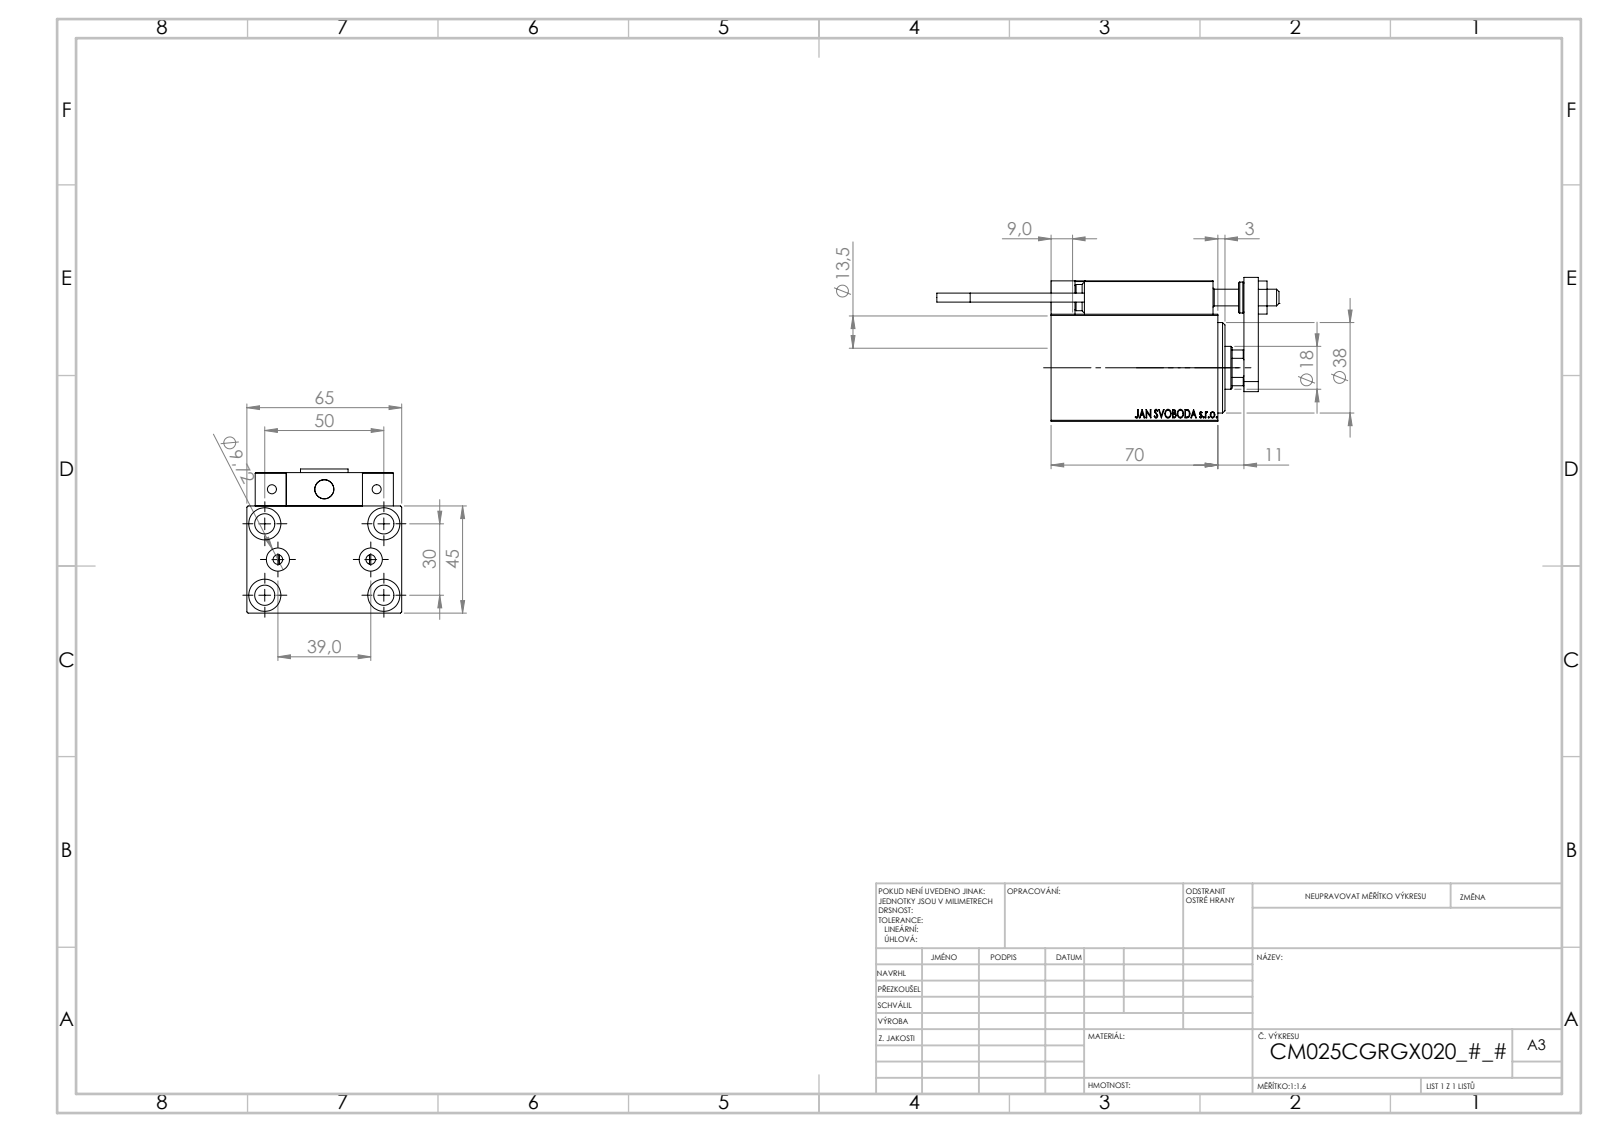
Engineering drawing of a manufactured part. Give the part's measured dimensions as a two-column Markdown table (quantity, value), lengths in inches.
| quantity | value |
| --- | --- |
| part name | TYC_L79; V450CM_VC_B; NUT_D12; SWITCH DIM B,W (+7 more) |
| STEP written by | SolidWorks 2019 (CONFIG_CONTROL_DESIGN) |
| units | inches |
| bodies | 23 solids, 1278 faces (560 planar, 184 cylindrical, 534 other) |
| overall size | 5.657 × 2.559 × 2.382 |
| volume | 13.67 in³ |
| surface area | 110.9 in² |
| round holes (diameter × count) | 0.157 × 6, 0.315 × 5, 0.335 × 5, 0.126 × 4, 0.531 × 4, 0.197 × 2, 0.383 × 2, 0.276 × 1, 0.571 × 1, 0.709 × 1, 0.846 × 1, 0.984 × 1 |
| round bosses / shafts (diameter × count) | 0.197 × 2, 0.15 × 2, 0.512 × 1, 0.433 × 1 |
| partial cylindrical surfaces (radius × count) | 0.012 × 30, 0.118 × 2, 0.335 × 1 |
| main face-to-face distances | 1.772, 2.559, 2.323, 0.551, 0.236, 0.118, 0.276, 0.197, 0.748, 0.787 |
| hole center spacings | 0.629, 1.148, 1.849, 0.448, 0.768, 0.787, 0.87, 1.138 |
